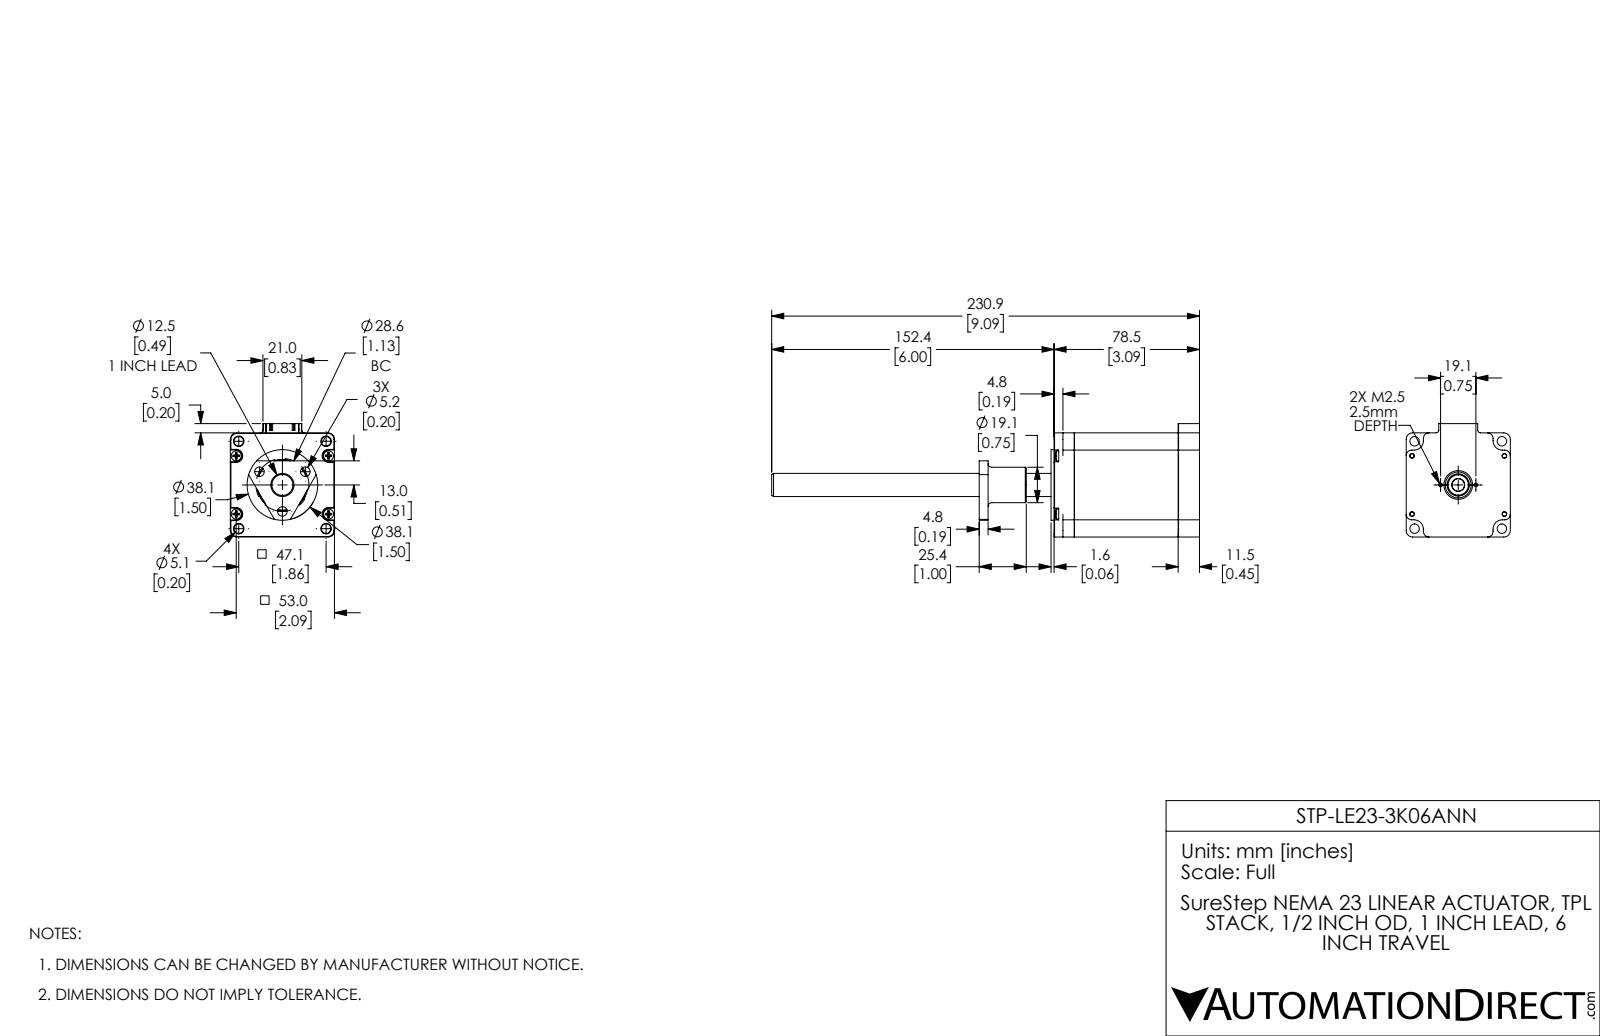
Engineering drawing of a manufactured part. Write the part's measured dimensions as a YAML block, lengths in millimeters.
part_name: "STP-LE23-3K06ANN_1; STP-LE23-3K06ANN_2; STP-LE23-3K06ANN"
step_written_by: "SolidWorks 2017 (AUTOMOTIVE_DESIGN)"
units: millimeters
bodies: {solids: 7, faces: 908, planar: 351, cylindrical: 400, other: 157}
overall_size: [230.9, 61.2, 56.2]
volume: 226610
surface_area: 61373
round_holes:
  - {diameter: 4.5, count: 8}
  - {diameter: 2.5, count: 4}
  - {diameter: 3.3, count: 4}
  - {diameter: 5.1, count: 4}
  - {diameter: 5.16, count: 3}
  - {diameter: 2, count: 2}
  - {diameter: 2.05, count: 2}
  - {diameter: 6.9, count: 1}
  - {diameter: 10.5, count: 1}
  - {diameter: 15.5, count: 1}
  - {diameter: 20, count: 1}
  - {diameter: 24, count: 1}
round_bosses_or_shafts:
  - {diameter: 5.4, count: 4}
  - {diameter: 2.91, count: 4}
  - {diameter: 38.1, count: 1}
  - {diameter: 36, count: 1}
  - {diameter: 35.6, count: 1}
  - {diameter: 34.85, count: 1}
  - {diameter: 28, count: 1}
  - {diameter: 19.1, count: 1}
partial_cylinders:
  - {radius: 1.5, count: 10}
  - {radius: 3, count: 8}
  - {radius: 1.8, count: 4}
  - {radius: 3.2, count: 4}
  - {radius: 3.5, count: 4}
  - {radius: 5, count: 4}
  - {radius: 0.6, count: 1}
  - {radius: 1.24, count: 1}
face_to_face_distances: [56.2, 56, 11.5, 67.5, 78.5, 11, 51.4, 67, 1.6, 1.1]
hole_center_spacings: [24.75, 14.12, 33.05, 35.01, 45.74, 48.53, 56.99, 6.55]
